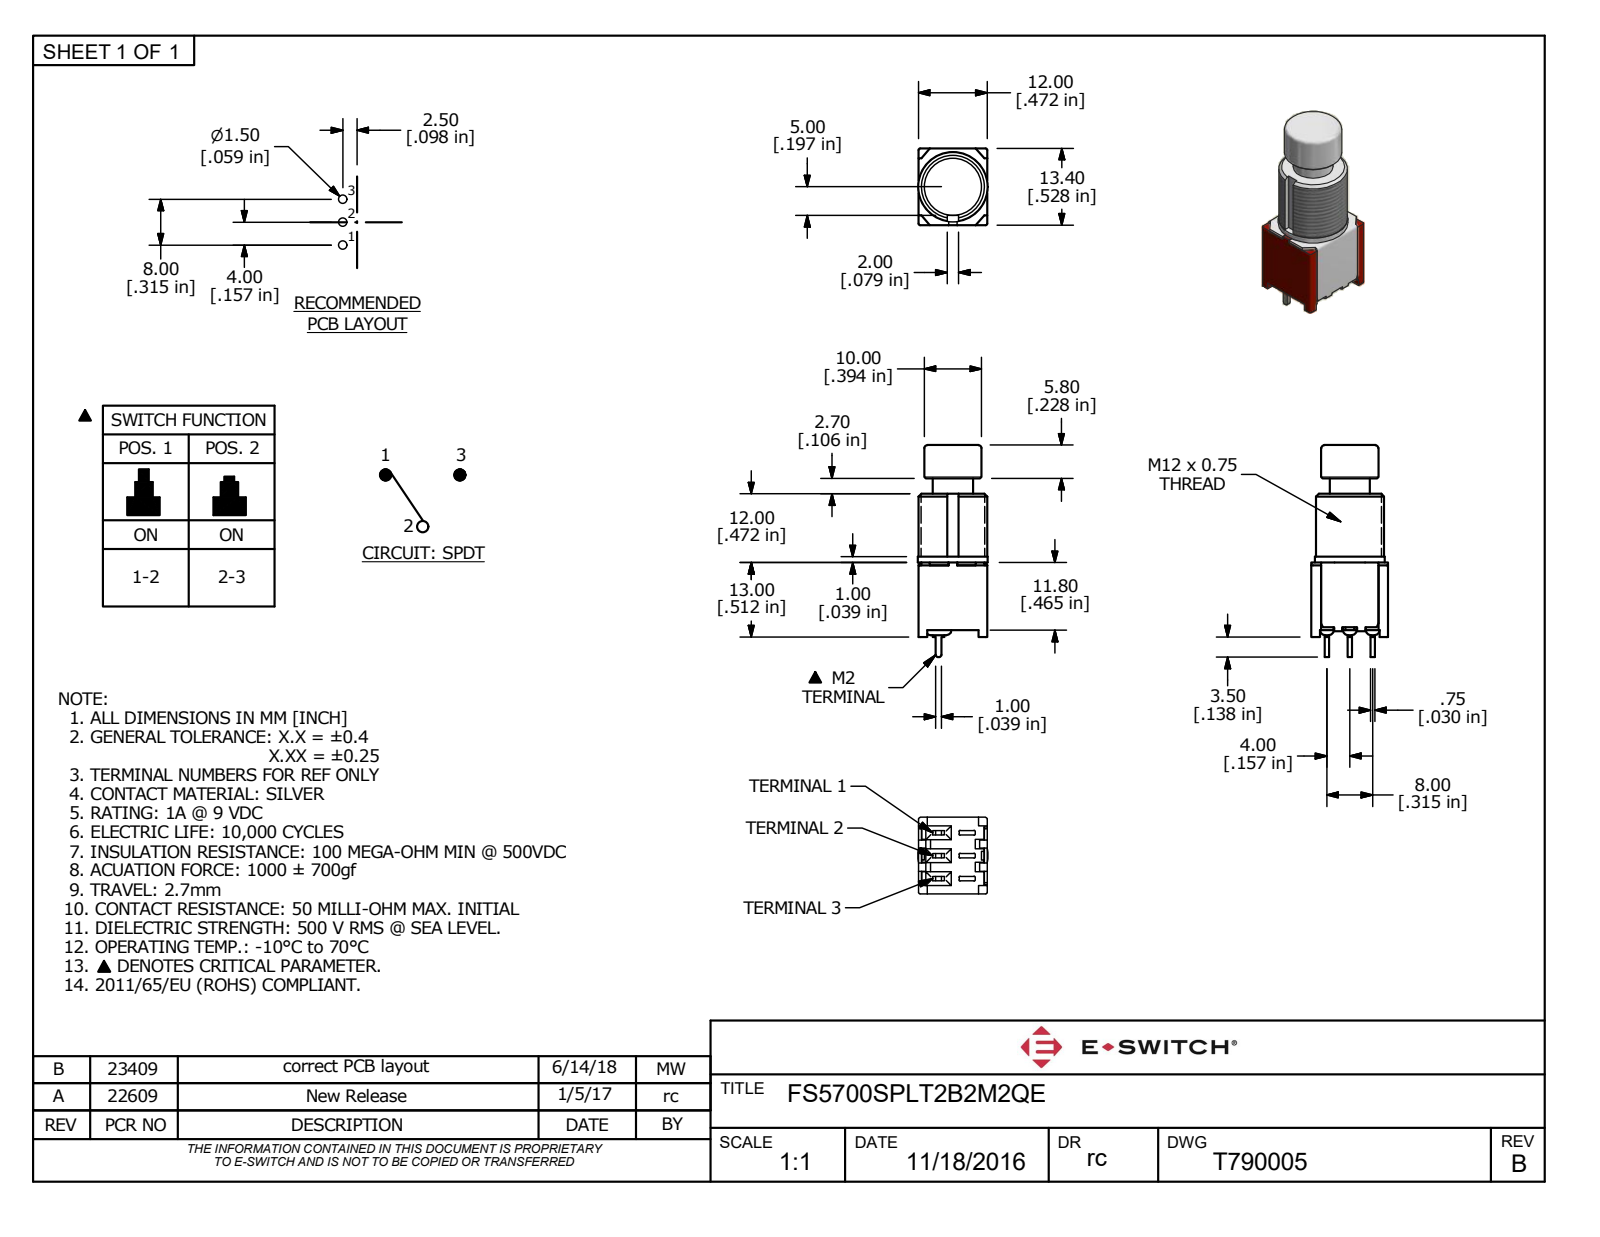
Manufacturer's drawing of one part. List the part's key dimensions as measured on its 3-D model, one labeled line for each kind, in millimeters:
Part name (STEP PRODUCT): FS5700SPLT2B2M2QE
STEP written by: Autodesk Inventor 2022 (AUTOMOTIVE_DESIGN)
Units: millimetres
Bodies: 1 solid, 277 faces (209 planar, 65 cylindrical, 3 other)
Overall size (bounding box): 37 × 13.4 × 12.2
Volume: 2 100 mm³ · Surface area: 3 258 mm²
Round holes (diameter × count): ⌀9 ×1
Round bosses / shafts (diameter × count): ⌀12.2 ×1, ⌀12 ×1, ⌀10 ×1, ⌀7 ×1
Partial cylindrical surfaces — rounded edges, fillets, slot ends (radius × count): R0.2 ×26, R0.9 ×8, R0.3 ×4, R0.5 ×4, R0.1 ×2, R0.4 ×2
Main face-to-face distances: 1.2, 0.5, 11, 10.8, 10.3, 0.7, 11.5, 0.55, 11.45, 0.65
